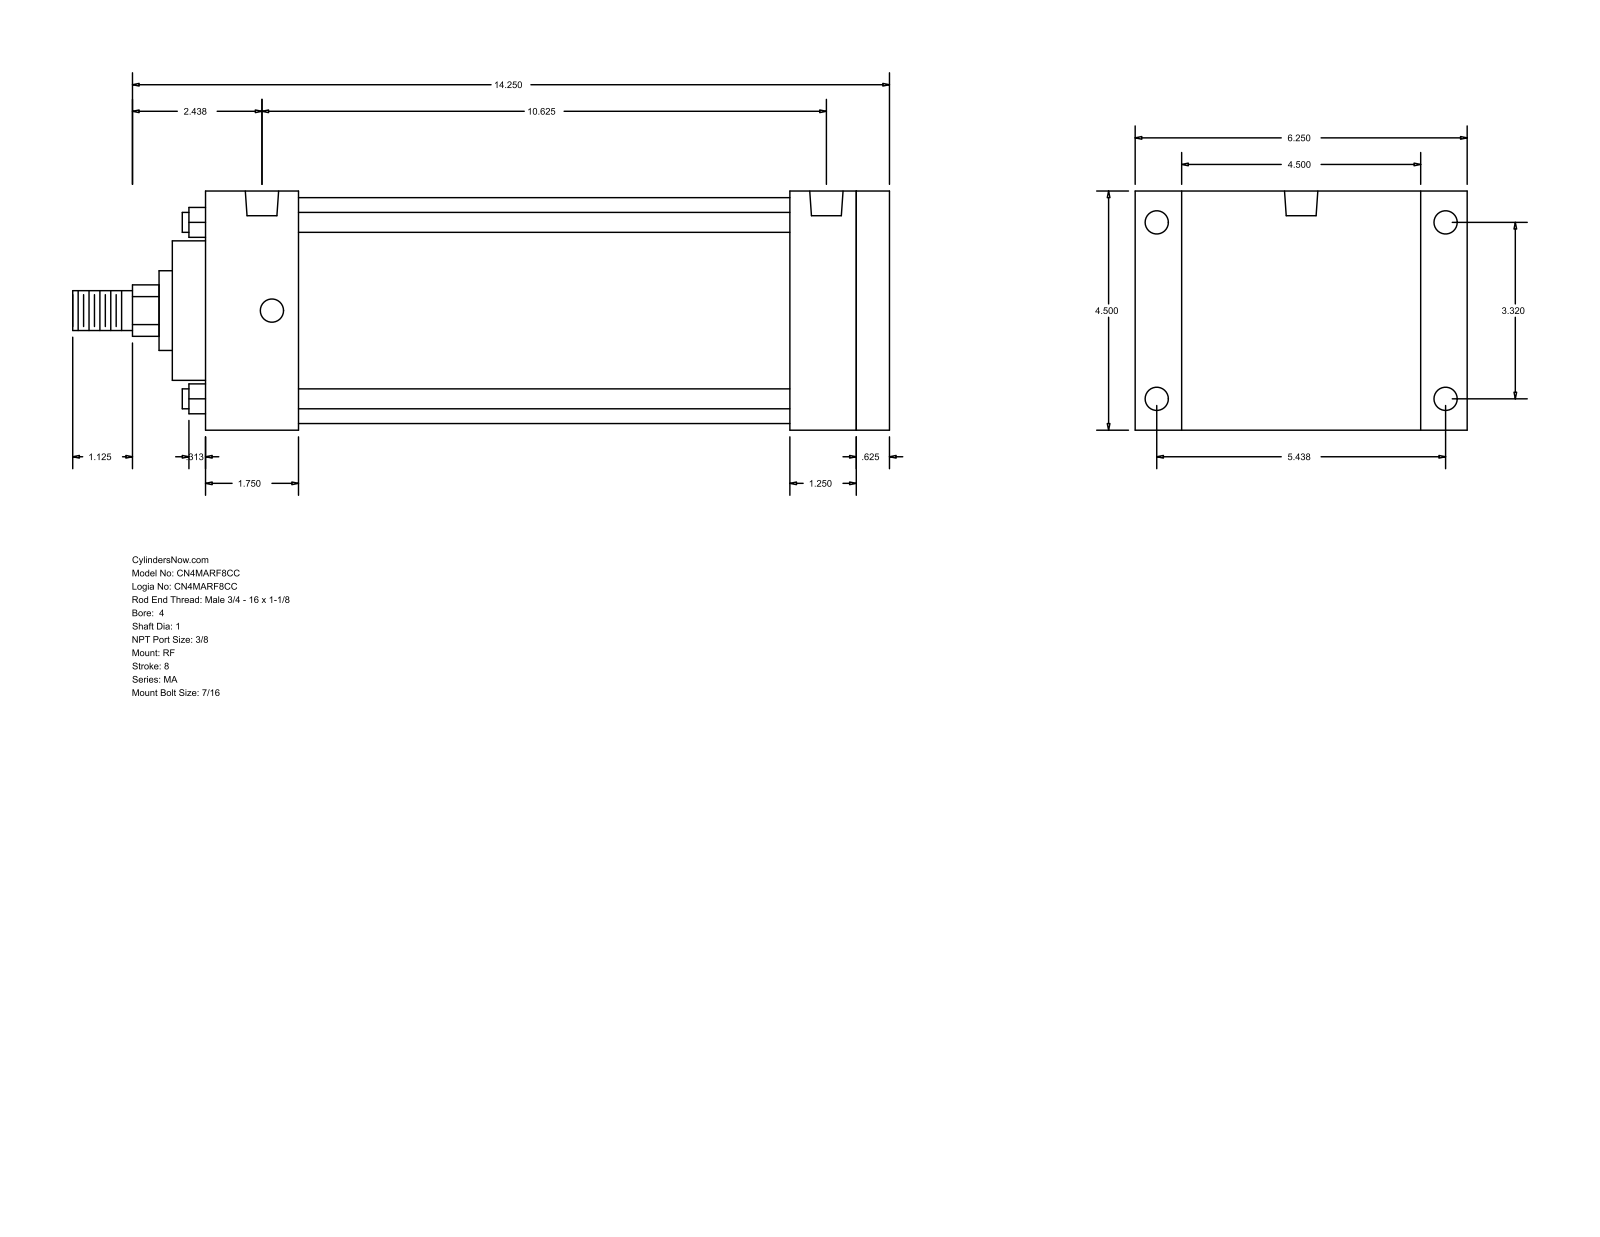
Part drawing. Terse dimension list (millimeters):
name: MA_RF__0400_1
written by: GSSL Pune (CONFIG_CONTROL_DESIGN)
unit: mm
bodies: 0 solids, 94 faces (65 planar, 29 cylindrical, 0 other)
size: 390.52 × 158.75 × 114.3
holes: 8× ⌀11.11, 2× ⌀15.93
bosses: 4× ⌀9.53, 1× ⌀107.95, 1× ⌀66.67, 1× ⌀38.1, 1× ⌀25.4, 1× ⌀19.05
rounds: 1× R12.29
face distances: 114.3, 327.03, 311.15, 15.88, 22.23, 136.53, 279.4, 31.75, 47.63, 44.46
hole spacings: 84.32, 138.12, 161.82, 260.35, 4.76, 4.77, 265.11, 265.12
